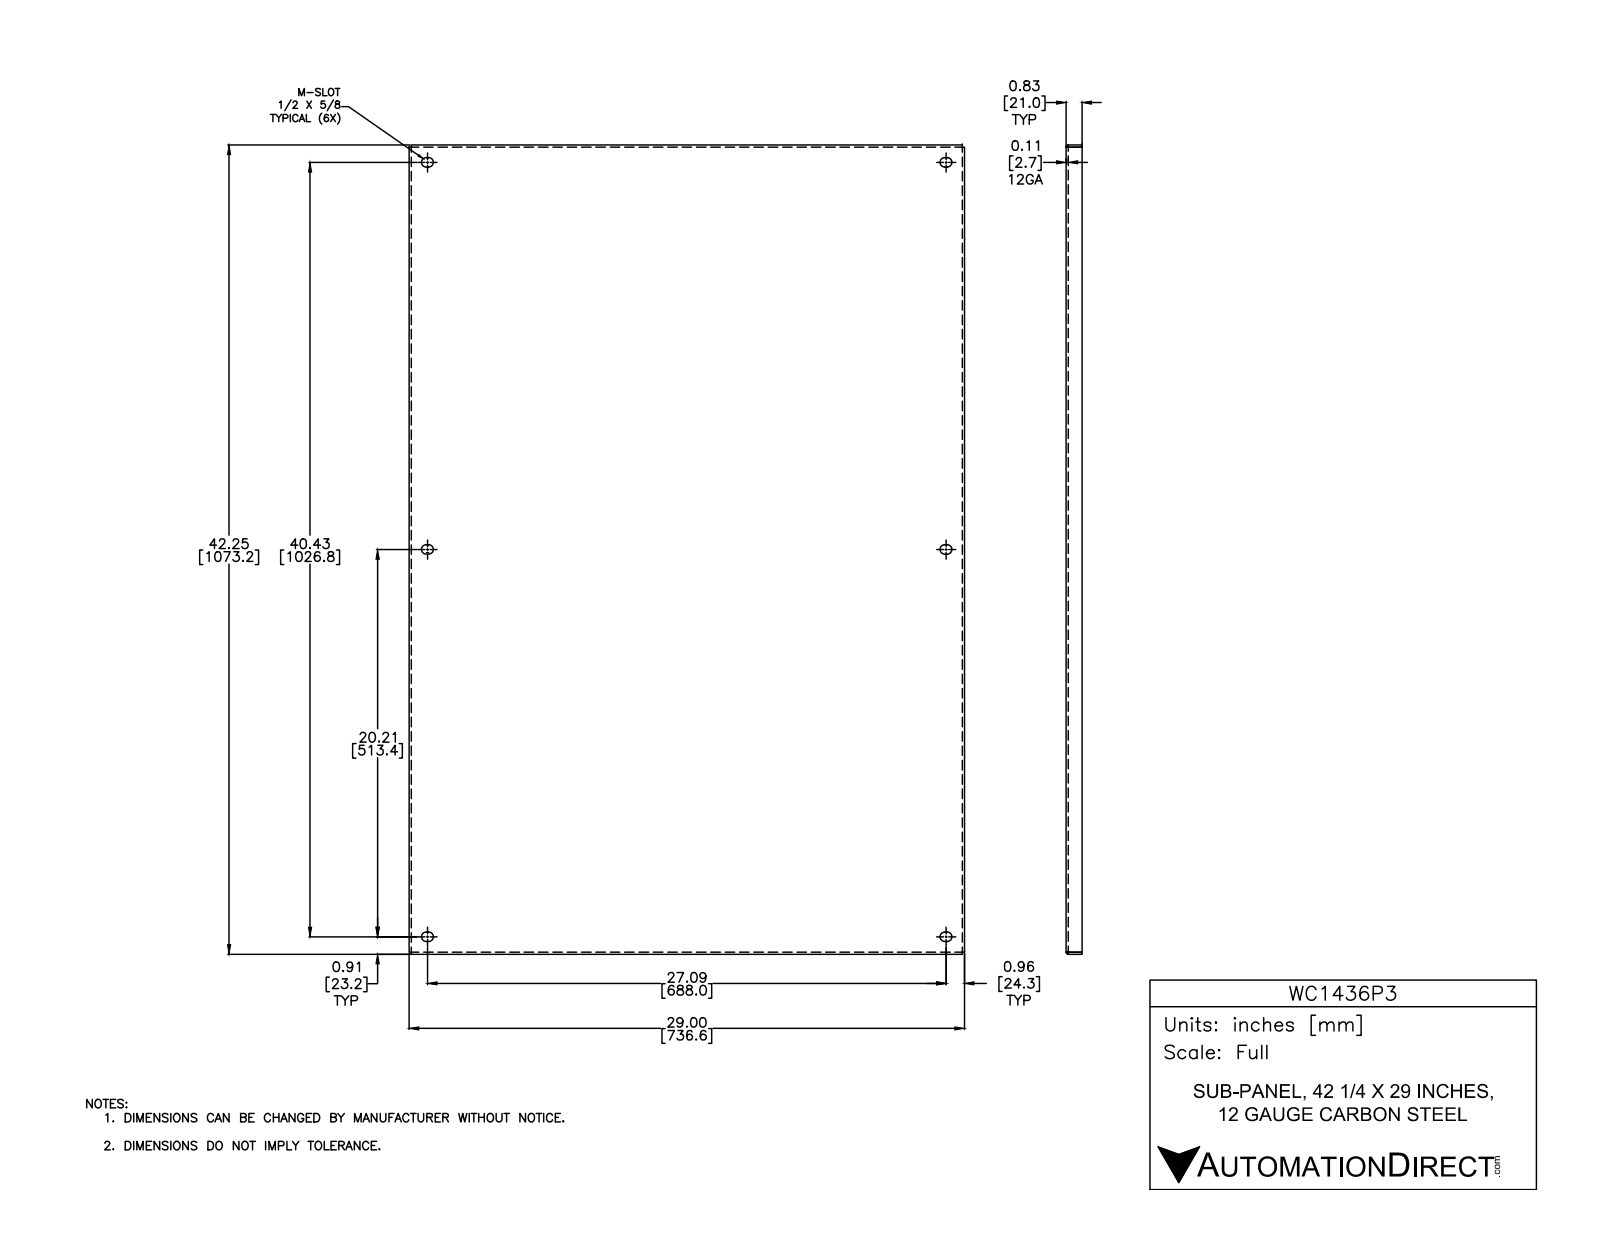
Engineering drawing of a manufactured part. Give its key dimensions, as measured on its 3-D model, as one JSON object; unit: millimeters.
{"part_name": "WC1436P3", "step_written_by": "SolidWorks 2014 (AUTOMOTIVE_DESIGN)", "units": "millimeters", "bodies": {"solids": 1, "faces": 68, "planar": 34, "cylindrical": 26, "other": 8}, "overall_size": [1077.9, 739.8, 21], "volume_mm3": 2286000, "surface_area_mm2": 1732000, "partial_cylinders_radius": [[6.4, 12], [2.7, 3], [2.7, 1]], "face_to_face_distances": [2.7, 2.6, 737.1, 739.8, 734.5, 737.1, 1075.3, 1077.9, 1072.6, 1075.3]}
